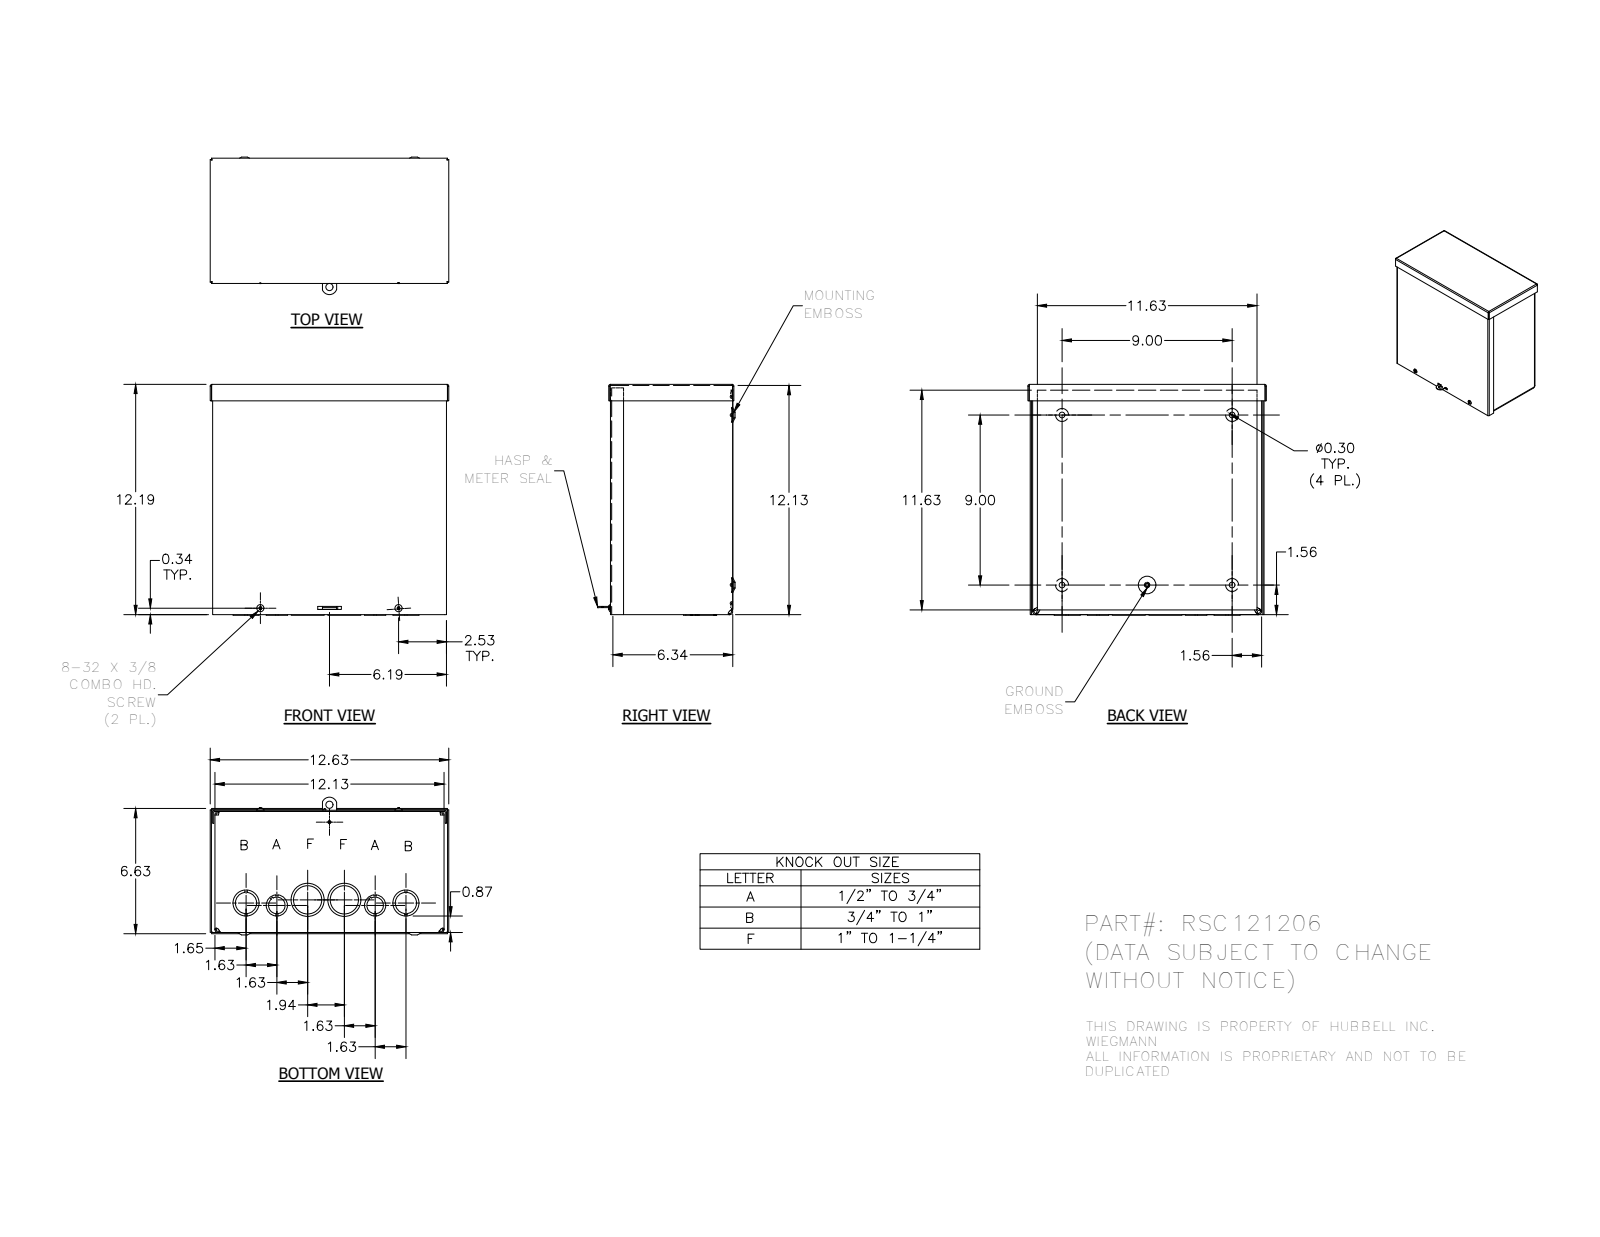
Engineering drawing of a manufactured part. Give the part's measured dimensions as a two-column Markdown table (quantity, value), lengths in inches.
| quantity | value |
| --- | --- |
| part name | RSC121206; RSC121206_WRAP; RSC1212_LID; RSC1206_CAP (+4 more) |
| STEP written by | Autodesk Inventor 2012 (AUTOMOTIVE_DESIGN) |
| units | inches |
| bodies | 7 solids, 551 faces (264 planar, 143 cylindrical, 144 other) |
| overall size | 12.625 × 12.281 × 7.125 |
| volume | 48.35 in³ |
| surface area | 1 579 in² |
| round holes (diameter × count) | 0.3 × 4, 0.313 × 4, 1.125 × 4, 0.125 × 2, 0.148 × 2, 0.875 × 2, 1.375 × 2, 1.5 × 2, 1.75 × 2, 0.156 × 1, 0.165 × 1, 0.375 × 1 |
| round bosses / shafts (diameter × count) | 0.384 × 2, 0.164 × 2, 0.229 × 1 |
| partial cylindrical surfaces (radius × count) | 0.01 × 14, 0.031 × 8, 0.093 × 8, 0.125 × 8, 0.187 × 8, 0.031 × 6, 0.025 × 5, 0.055 × 4 |
| main face-to-face distances | 0.062, 12.126, 0.062, 6.249, 6.187, 0.063, 12.188, 6.312, 6.25, 0.124 |
| hole center spacings | 9, 1.356, 1.635, 1.656, 3.264, 3.582, 4.5, 5.203 |
